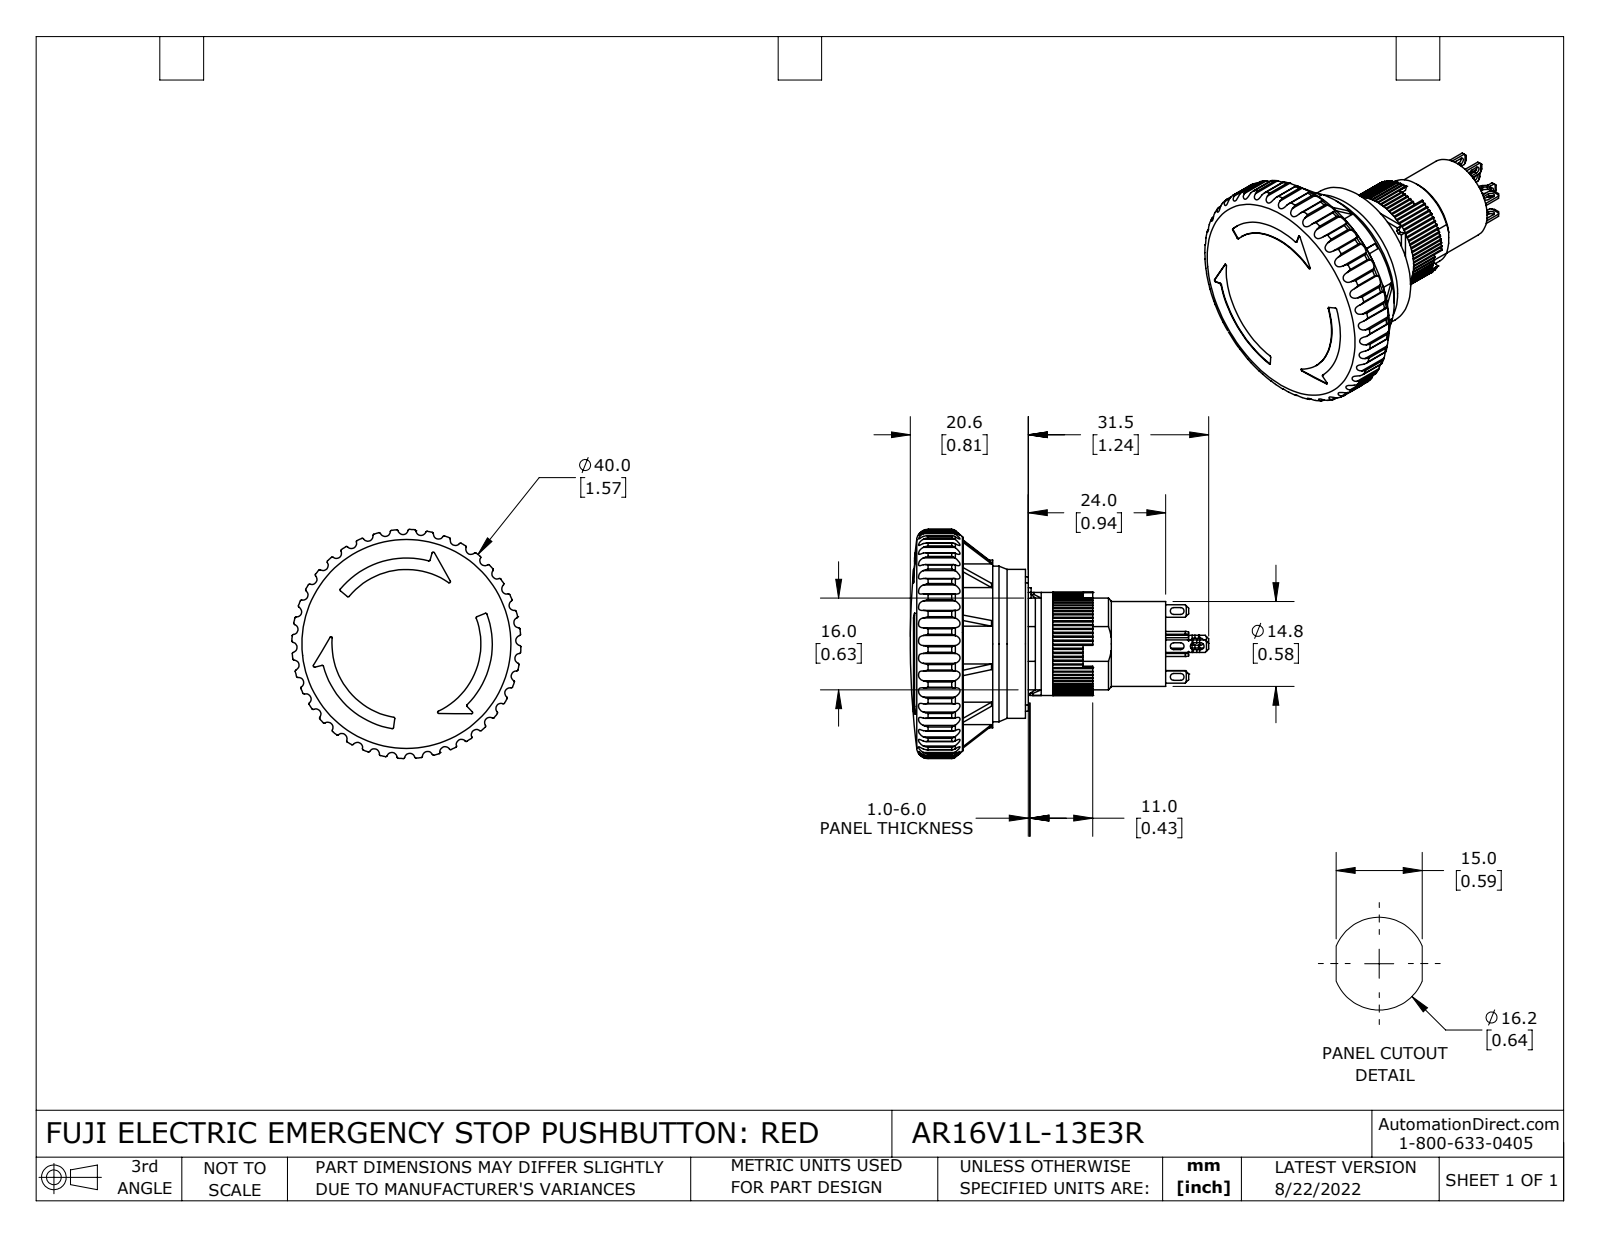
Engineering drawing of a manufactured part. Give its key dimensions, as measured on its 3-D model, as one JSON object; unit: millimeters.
{"part_name": "AR16V1L-13E3R", "step_written_by": "SolidWorks 2021 (CONFIG_CONTROL_DESIGN)", "units": "millimeters", "bodies": {"solids": 7, "faces": 1081, "planar": 547, "cylindrical": 438, "other": 96}, "overall_size": [52.1, 40, 40], "volume_mm3": 15800, "surface_area_mm2": 12370, "round_holes": [[14.8, 1], [16, 1], [18, 1], [27.2, 1], [36.4, 1]], "round_bosses_or_shafts": [[29.3, 1], [26, 1], [21.8, 1], [6, 1]], "partial_cylinders_radius": [[0.2, 80], [0.3, 80], [0.9, 40], [0.6, 16], [0.5, 8], [0.3, 4], [0.7, 4], [1, 2]], "face_to_face_distances": [1, 10.7, 13.5, 2.7, 0.5, 1.8, 21.7, 12.4, 2.3, 1.2]}
